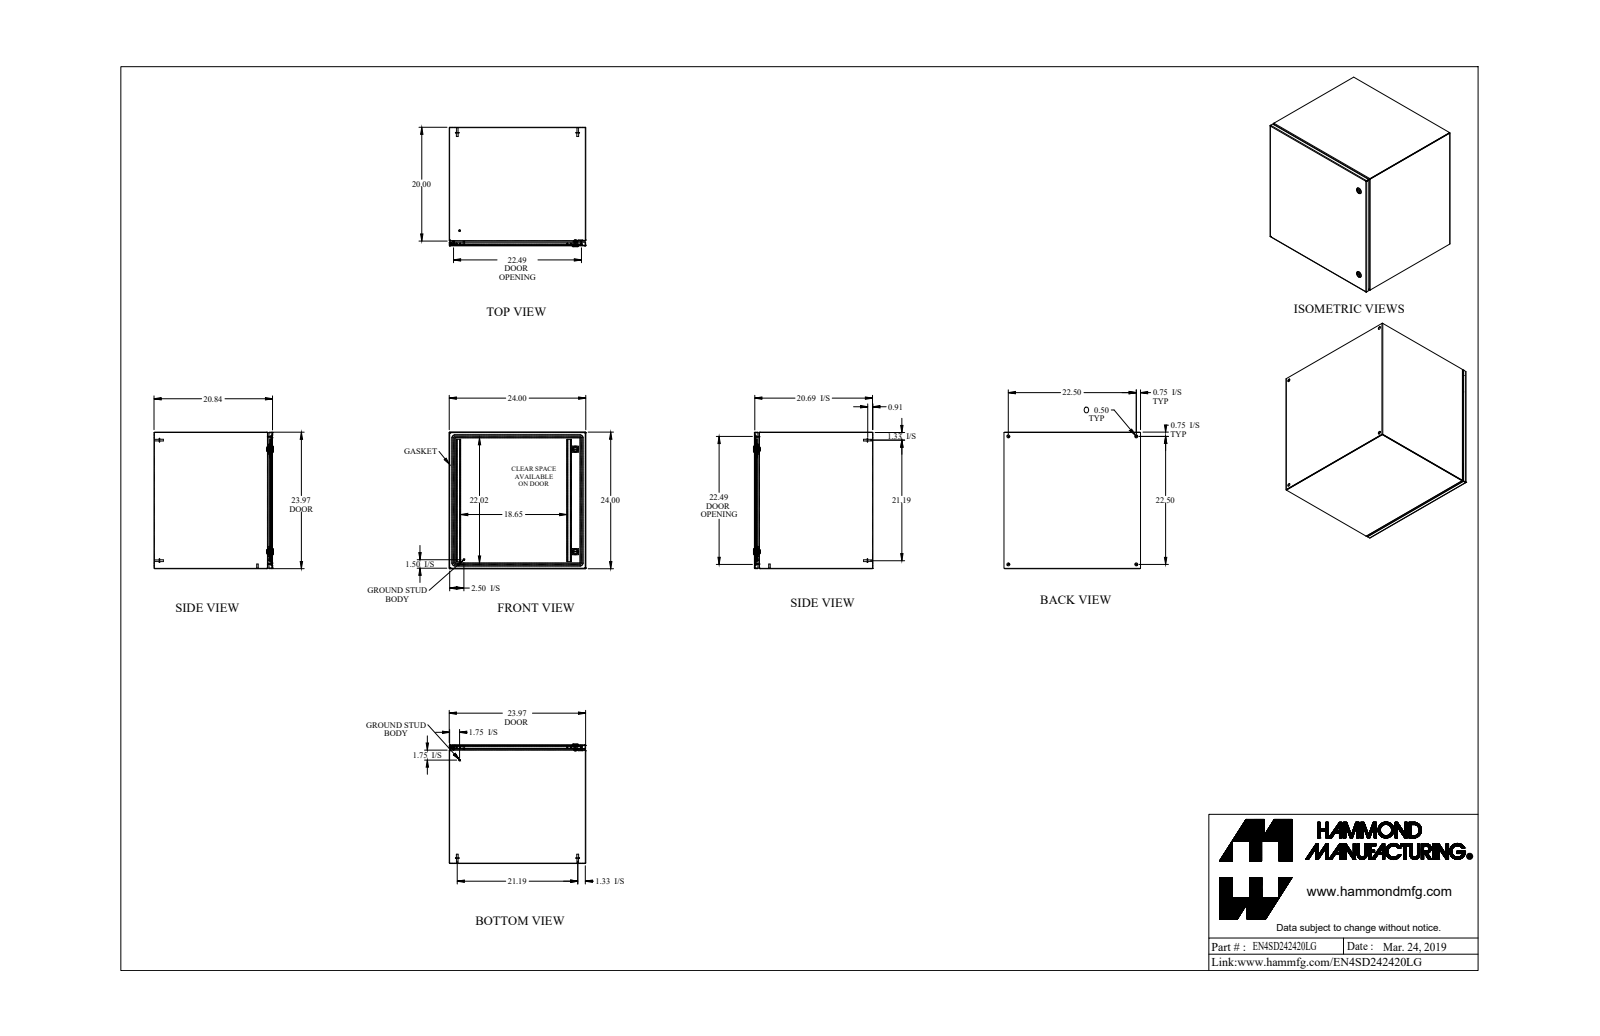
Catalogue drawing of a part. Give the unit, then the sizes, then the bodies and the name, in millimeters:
Units: millimetres
Overall size (bounding box): 609.6 × 609.6 × 533.3
Round holes (diameter × count): ⌀12.7 ×4, ⌀5.9 ×2, ⌀15.9 ×2, ⌀19.9 ×2, ⌀4.4 ×1, ⌀6.1 ×1, ⌀6.1 ×1
Round bosses / shafts (diameter × count): ⌀15.9 ×4, ⌀8 ×4, ⌀6.9 ×4, ⌀27.9 ×2, ⌀13.3 ×2, ⌀7.1 ×2, ⌀6.4 ×2, ⌀11.6 ×1
Partial cylindrical surfaces — rounded edges, fillets, slot ends (radius × count): R0.9 ×14, R2.7 ×14, R1.1 ×12, R2.1 ×12, R7.9 ×12, R2.5 ×8, R0.2 ×4, R1.6 ×4
Main face-to-face distances: 1.8, 607.8, 527.4, 605.9, 609.6, 525.6, 529.3, 21.3, 506.2, 19.1
Hole centre spacings: 571.5, 808.2, 63.3, 63.3, 457.2, 515, 515.1, 547.2
Volume: 4 036 000 mm³ · Surface area: 4 446 000 mm²
Bodies: 29 solids, 736 faces (363 planar, 245 cylindrical, 128 other)
Part name (STEP PRODUCT): EN4SD242420LG
STEP written by: SolidWorks 2019 (AUTOMOTIVE_DESIGN)
